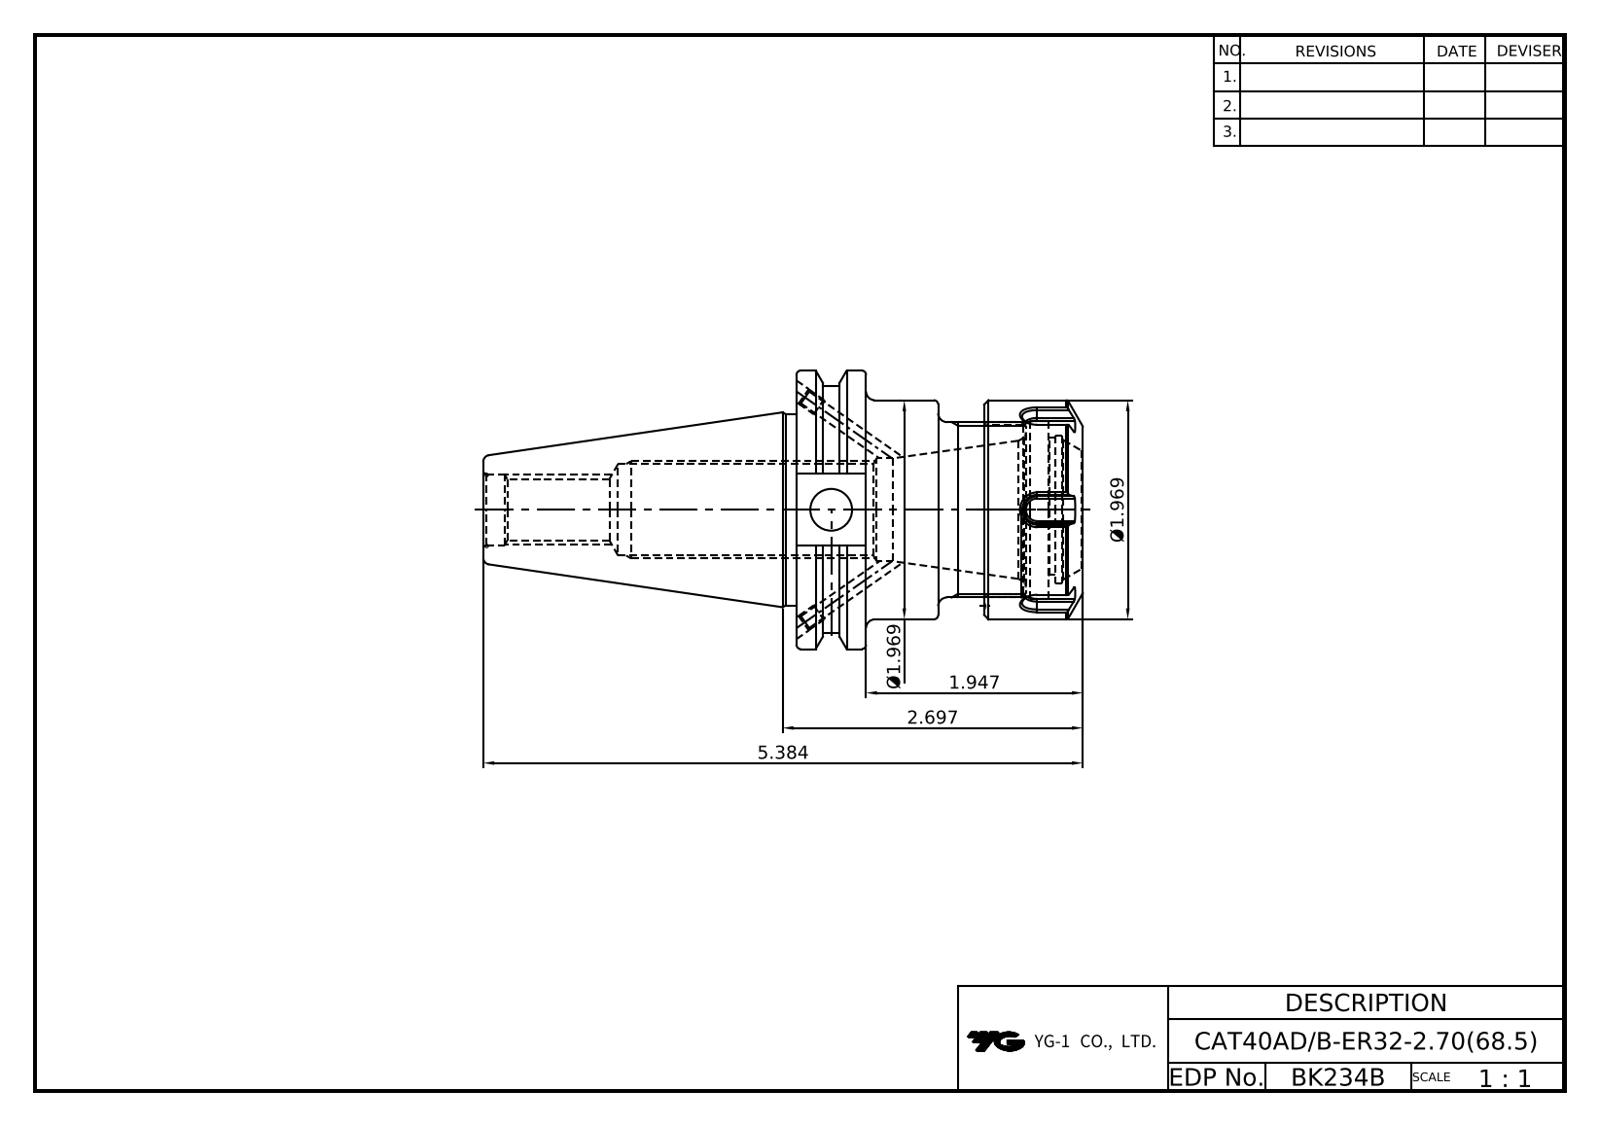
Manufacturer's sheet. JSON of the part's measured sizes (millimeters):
{"part_name": "LO-CAT40ADB-ER32-2; LO-CAT40ADB-ER32-2.70; ER32NUT", "step_written_by": "Autodesk Inventor 2025 (AUTOMOTIVE_DESIGN)", "units": "millimeters", "bodies": {"solids": 2, "faces": 159, "planar": 69, "cylindrical": 38, "other": 52}, "overall_size": [136.75, 63.5, 61.09], "volume_mm3": 143907, "surface_area_mm2": 38049, "round_holes": [[3.24, 2], [4, 2], [1, 1], [9.53, 1], [13.39, 1], [16.3, 1], [20.5, 1], [23.5, 1], [27.1, 1], [31.4, 1], [33.8, 1], [38.6, 1]], "round_bosses_or_shafts": [[63.5, 1], [56.3, 1], [50, 1], [43.6, 1], [40, 1]], "partial_cylinders_radius": [[0.5, 12], [8.19, 1]], "face_to_face_distances": [65.33, 15.88, 49.45, 42.83, 26.95, 22.5, 57.43, 41.55, 14.6, 7.9], "hole_center_spacings": [0.48, 0.74, 0.8, 22, 22.2, 22.8]}
